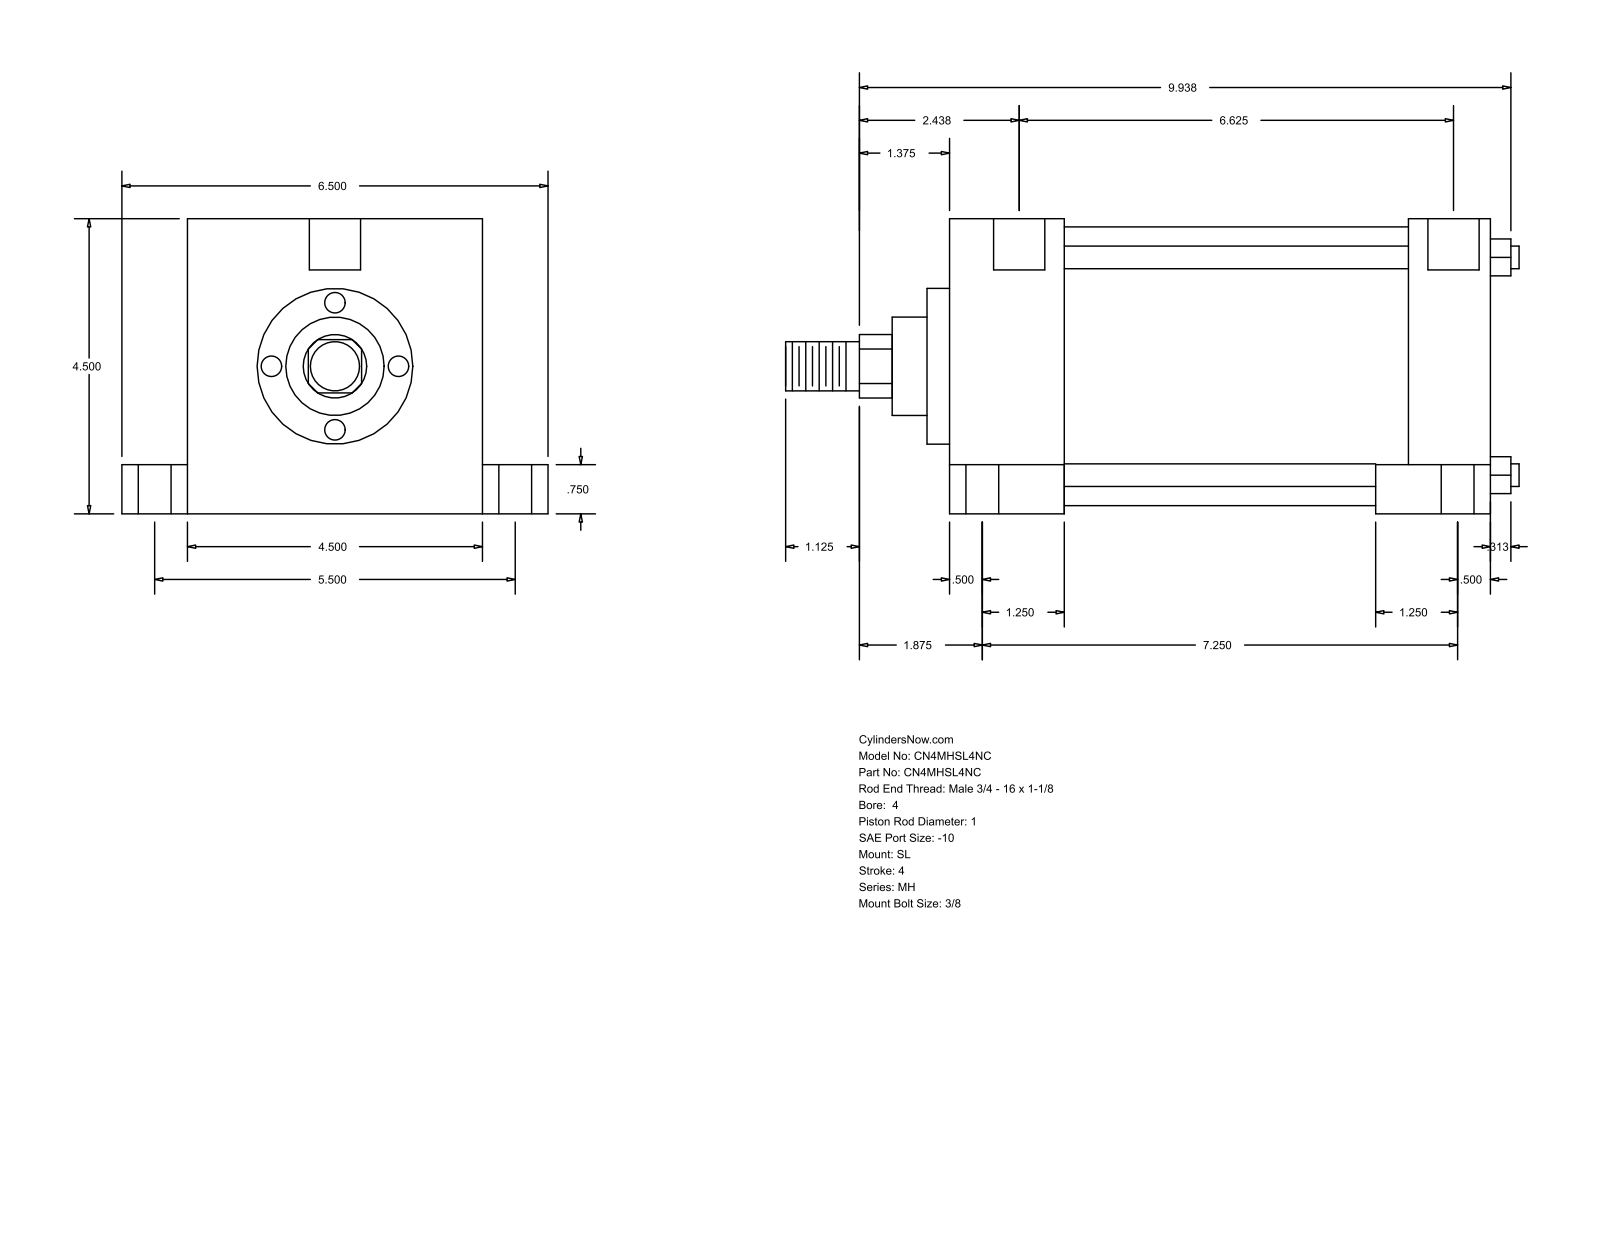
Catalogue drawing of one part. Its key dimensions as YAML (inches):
part_name: "MH_SL__0400_1"
step_written_by: "GSSL Pune (CONFIG_CONTROL_DESIGN)"
units: inches
bodies: {solids: 0, faces: 110, planar: 77, cylindrical: 33, other: 0}
overall_size: [11.187, 6.5, 4.5]
round_holes:
  - {diameter: 0.344, count: 4}
  - {diameter: 0.5, count: 4}
  - {diameter: 0.75, count: 4}
  - {diameter: 0.781, count: 2}
round_bosses_or_shafts:
  - {diameter: 0.345, count: 4}
  - {diameter: 4.25, count: 1}
  - {diameter: 2.375, count: 1}
  - {diameter: 1.5, count: 1}
  - {diameter: 1, count: 1}
  - {diameter: 0.75, count: 1}
partial_cylinders:
  - {radius: 0.484, count: 1}
face_to_face_distances: [4.5, 8.25, 1.75, 6.5, 7, 5.25, 1.25, 1, 5.5, 0.75]
hole_center_spacings: [2.75, 2.751, 2.795, 2.807, 5.5, 6.75, 7.231, 7.25]
